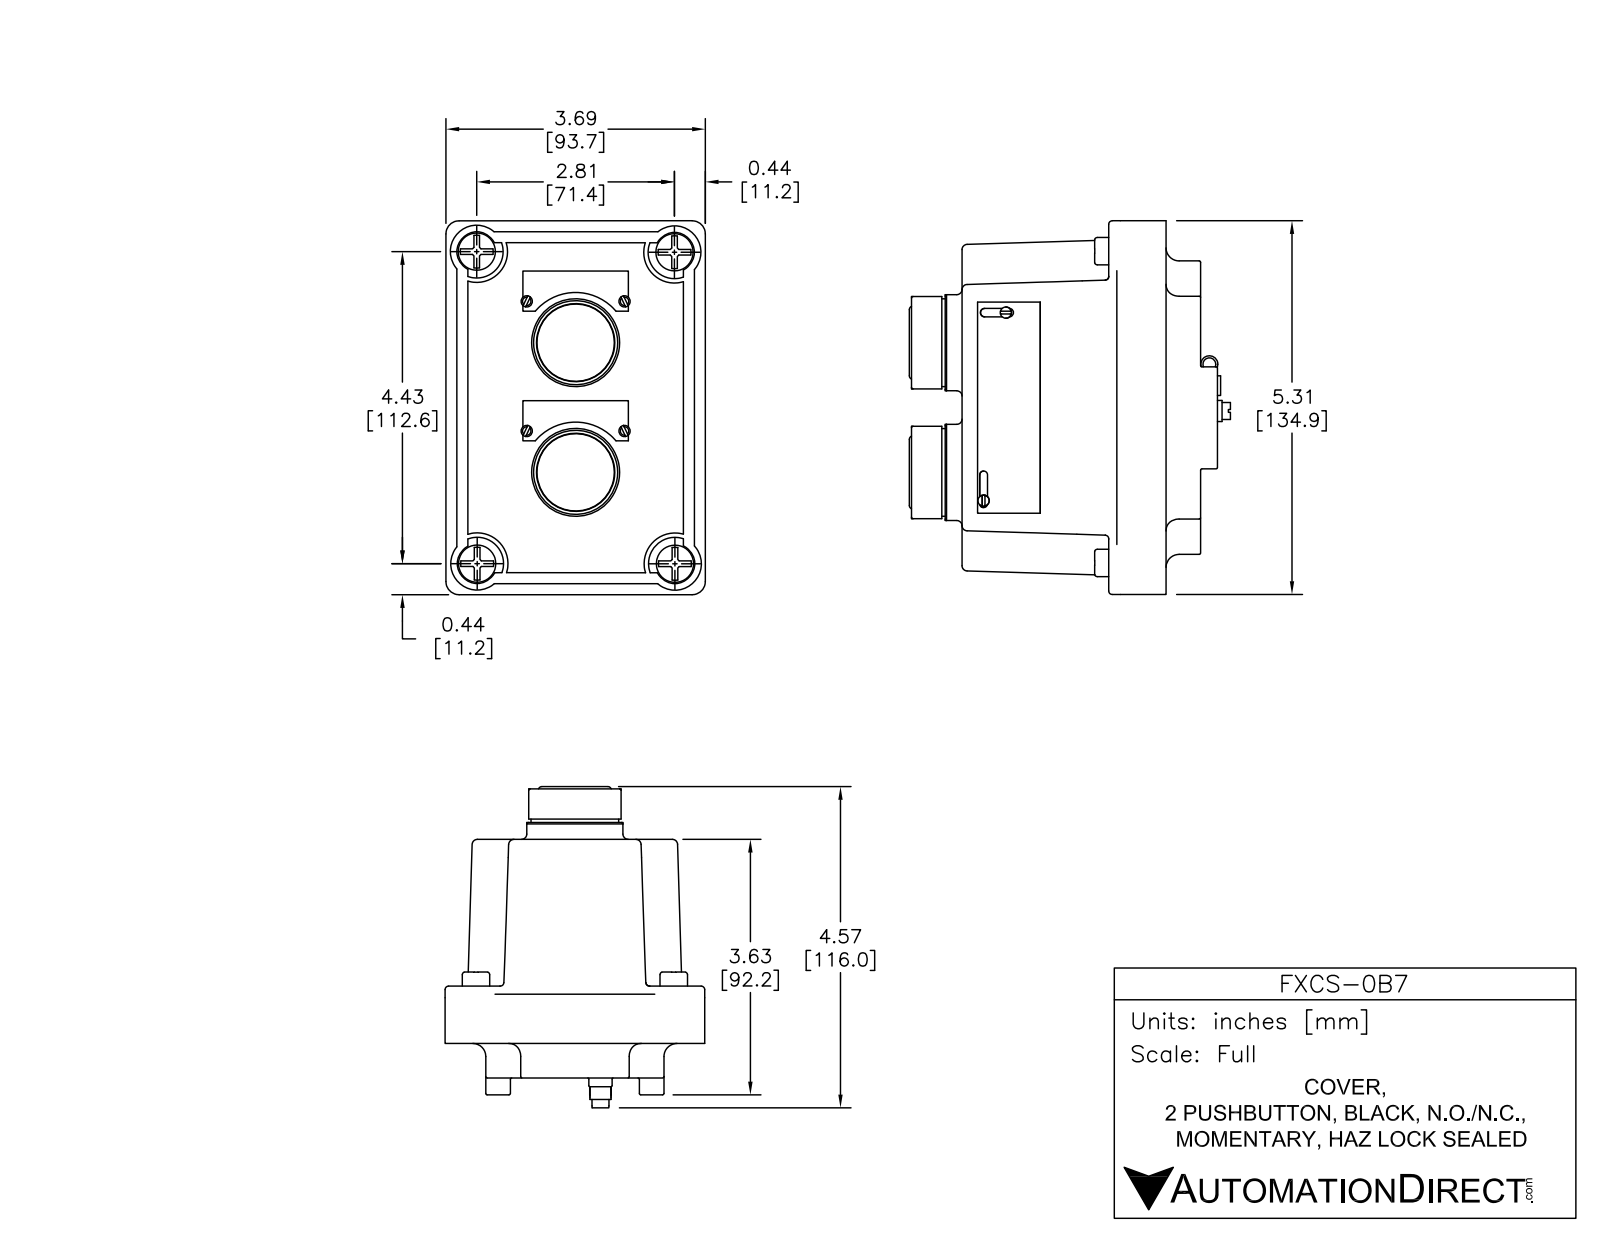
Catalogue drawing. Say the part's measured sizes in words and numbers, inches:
The part is named "FXCS-0B7". Its 3-D file was written by "SolidWorks 2015 (AUTOMOTIVE_DESIGN)". It is 1 solid with 741 faces: 305 planar, 163 cylindrical and 273 other. Overall it measures 5.31 by 4.639 by 3.69 inches. Its volume is 49.71 cubic inches and its surface area 109.3 square inches. Round holes: 8 of diameter 0.16, 2 of diameter 1.152, 1 of diameter 0.198. Round bosses or shafts: 8 of diameter 0.16, 4 of diameter 0.39, 2 of diameter 1.366, 2 of diameter 1.312, 2 of diameter 1.246, 2 of diameter 1.04, 1 of diameter 0.33, 1 of diameter 0.3. Partial cylindrical surfaces (rounded edges, fillets, slot ends): 22 of radius 0.02, 12 of radius 0.05, 4 of radius 0.055, 4 of radius 0.06, 4 of radius 0.075, 4 of radius 0.185, 4 of radius 0.42, 3 of radius 0.653. The main face-to-face distances are 3.39, 0.49, 2.9, 0.02, 3.69, 0.578, 3.111, 1.19, 0.7, 2.2. The hole center spacings are 0.25, 2.197, 0.5, 2.183, 2.239, 0.75, 1.205, 1.265.
